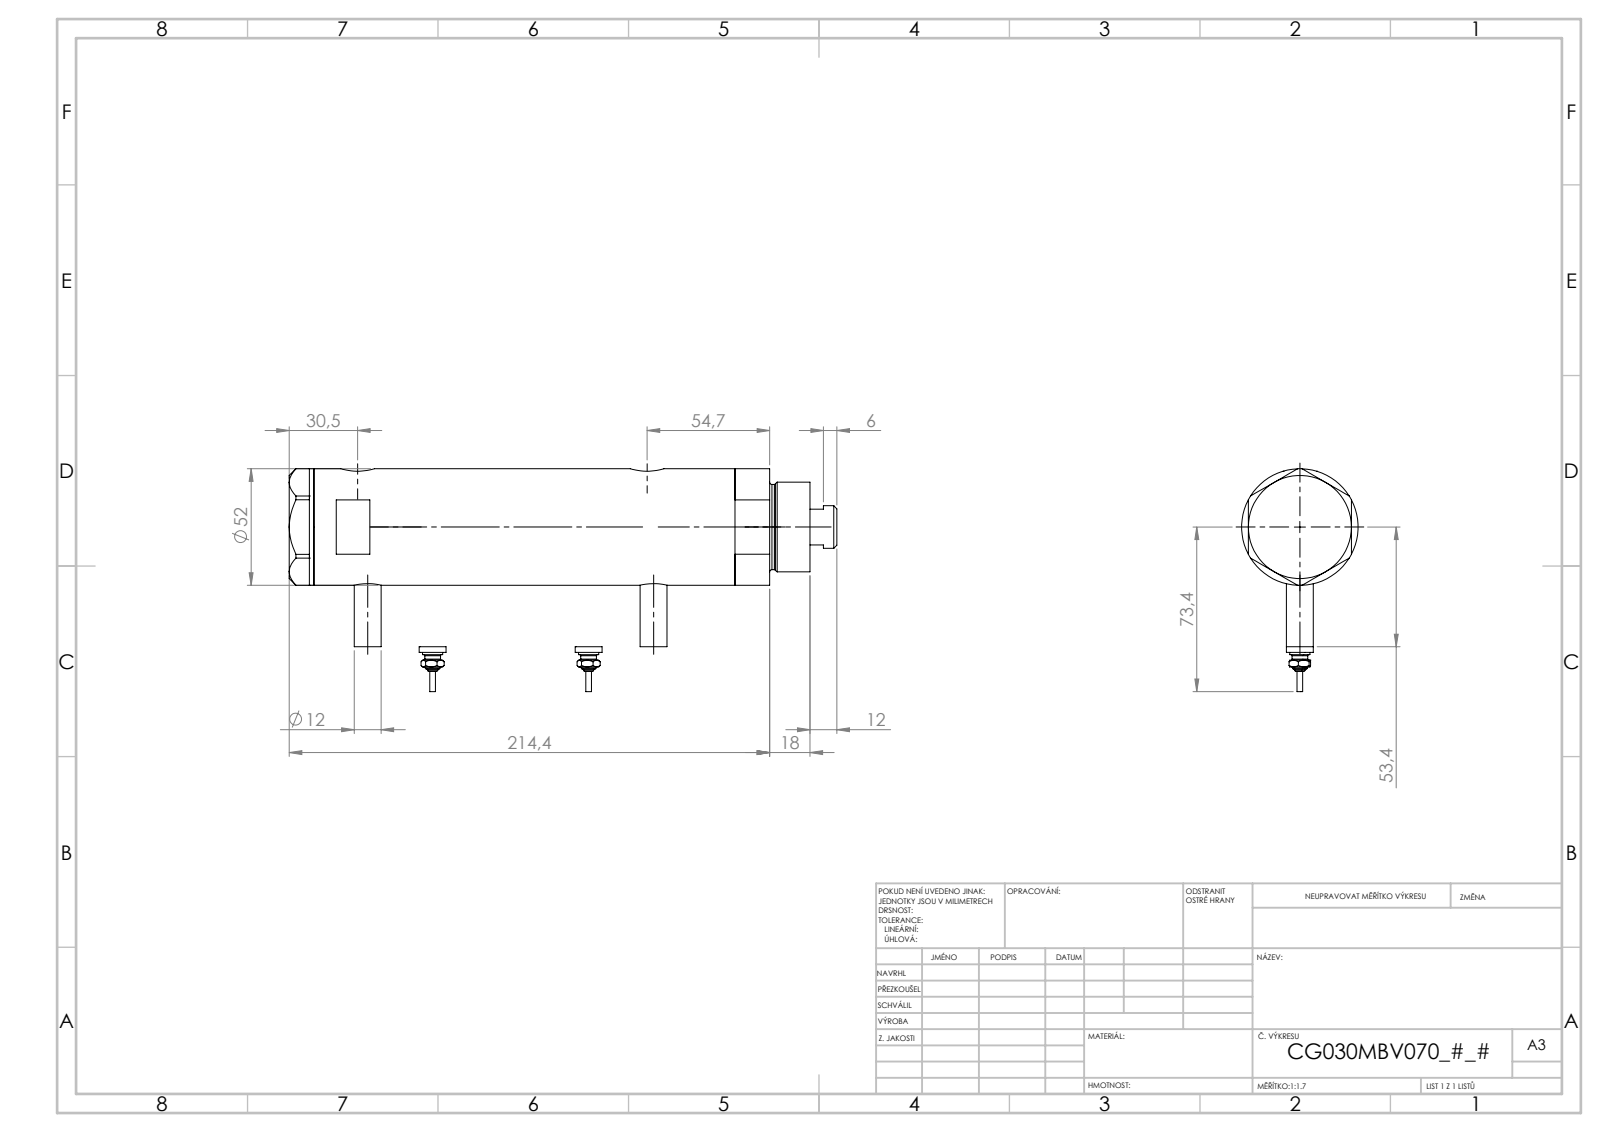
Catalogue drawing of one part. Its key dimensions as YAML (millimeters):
part_name: "V270CG_MIDDLE; V270CG_BACK; V270CG_VC; V270CG_FRONT (+1 more)"
step_written_by: "SolidWorks 2019 (CONFIG_CONTROL_DESIGN)"
units: millimeters
bodies: {solids: 6, faces: 246, planar: 95, cylindrical: 77, other: 74}
overall_size: [219.02, 84.3, 52]
volume: 391546
surface_area: 89467
round_holes:
  - {diameter: 5, count: 2}
  - {diameter: 9.73, count: 2}
  - {diameter: 12.5, count: 2}
  - {diameter: 15, count: 2}
  - {diameter: 6.5, count: 1}
  - {diameter: 20, count: 1}
  - {diameter: 21.5, count: 1}
  - {diameter: 30, count: 1}
  - {diameter: 33, count: 1}
  - {diameter: 44, count: 1}
round_bosses_or_shafts:
  - {diameter: 12, count: 3}
  - {diameter: 9, count: 2}
  - {diameter: 7, count: 2}
  - {diameter: 4.34, count: 2}
  - {diameter: 2.4, count: 2}
  - {diameter: 52, count: 1}
  - {diameter: 40, count: 1}
  - {diameter: 38, count: 1}
face_to_face_distances: [123.54, 23.8, 99.74, 11, 34.8, 134.54, 46, 170.94, 159.94, 136.14]
hole_center_spacings: [2.9, 4.5, 96.75, 99.65, 101.25, 104.15, 2.89, 2.91]
